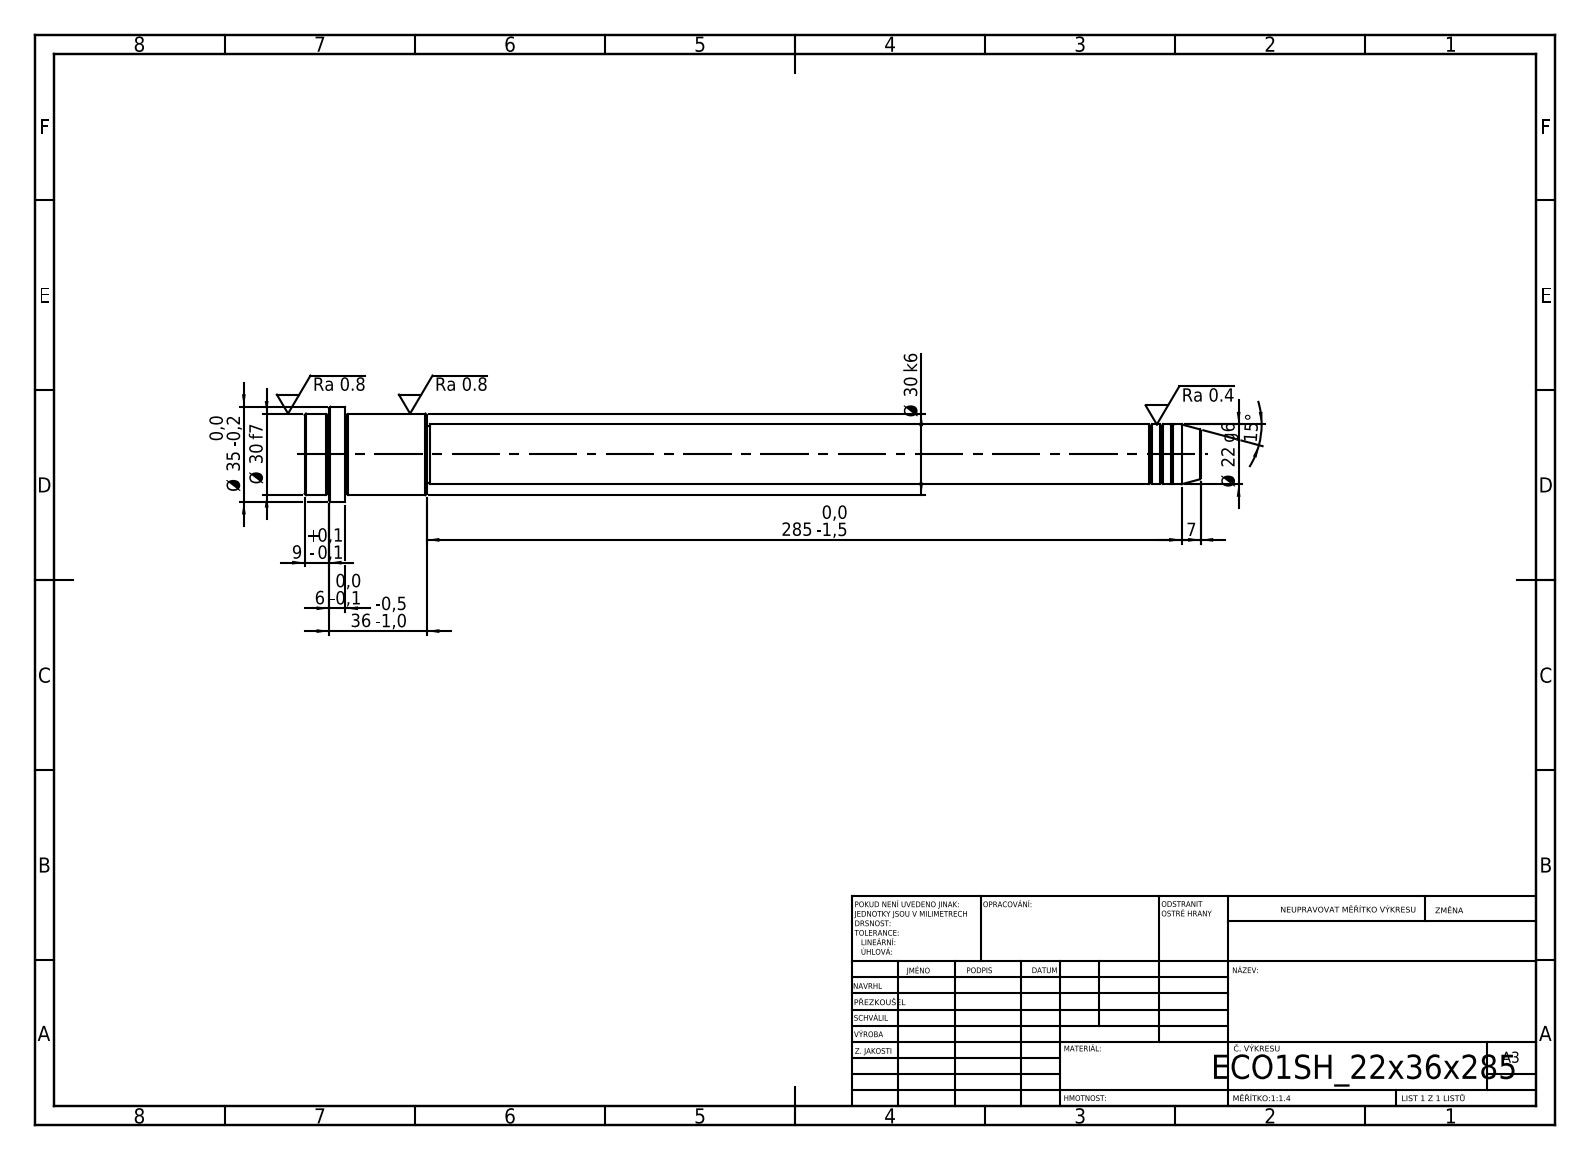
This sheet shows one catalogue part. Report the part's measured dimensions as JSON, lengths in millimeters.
{"step_written_by": "SolidWorks 2019 (CONFIG_CONTROL_DESIGN)", "units": "millimeters", "bodies": {"solids": 1, "faces": 52, "planar": 6, "cylindrical": 16, "other": 30}, "overall_size": [330, 35, 35], "volume_mm3": 141025, "surface_area_mm2": 25993, "round_bosses_or_shafts": [[35, 1], [30, 1], [22, 1], [21, 1]], "face_to_face_distances": [45, 30, 15, 285, 315, 330, 321, 36, 6, 9]}
